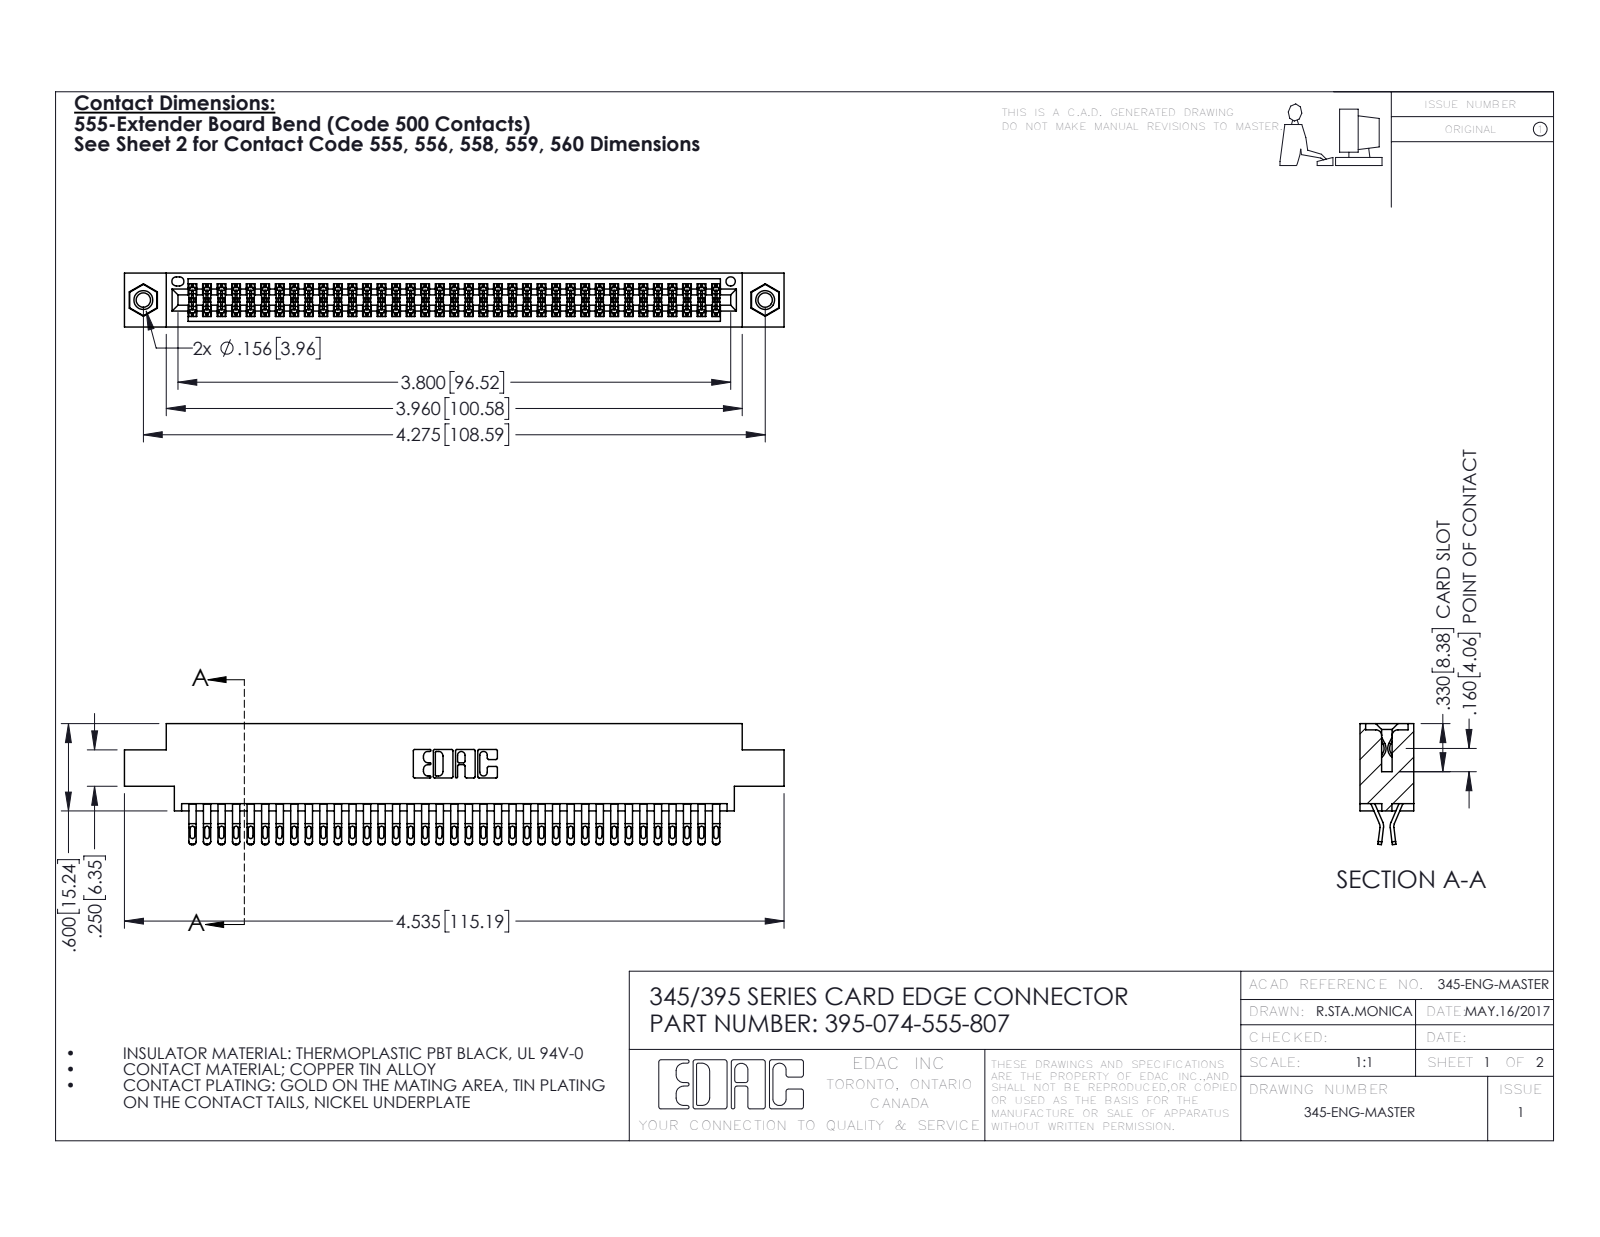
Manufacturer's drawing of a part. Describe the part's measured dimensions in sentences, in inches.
The part is named "395-074-555-807; 345-250-001_345-250-005-103; 345-292-001_555 Tail; 345 Part_0.170 Offset - 0.156 Dia-TI". Its 3-D file was written by "SolidWorks 2016 (CONFIG_CONTROL_DESIGN)". It is 77 solids with 4334 faces: 2410 planar, 1908 cylindrical and 16 other. Overall it measures 4.535 by 0.832 by 0.37 inches. Its volume is 0.685 cubic inches and its surface area 27 square inches. Round holes: 2 of diameter 0.098, 2 of diameter 0.125, 2 of diameter 0.156, 1 of diameter 0.064. Round bosses or shafts: 2 of diameter 0.155. Partial cylindrical surfaces (rounded edges, fillets, slot ends): 185 of radius 0.016, 148 of radius 0.02, 111 of radius 0.006, 22 of radius 0.01, 6 of radius 0.007, 6 of radius 0.031, 3 of radius 0.026, 2 of radius 0.01. The main face-to-face distances are 0.072, 0.298, 0.37, 0.025, 0.2, 0.098, 0.272, 0.225, 0.175, 0.149. The hole center spacings are 0.27, 4.039, 4.275.
